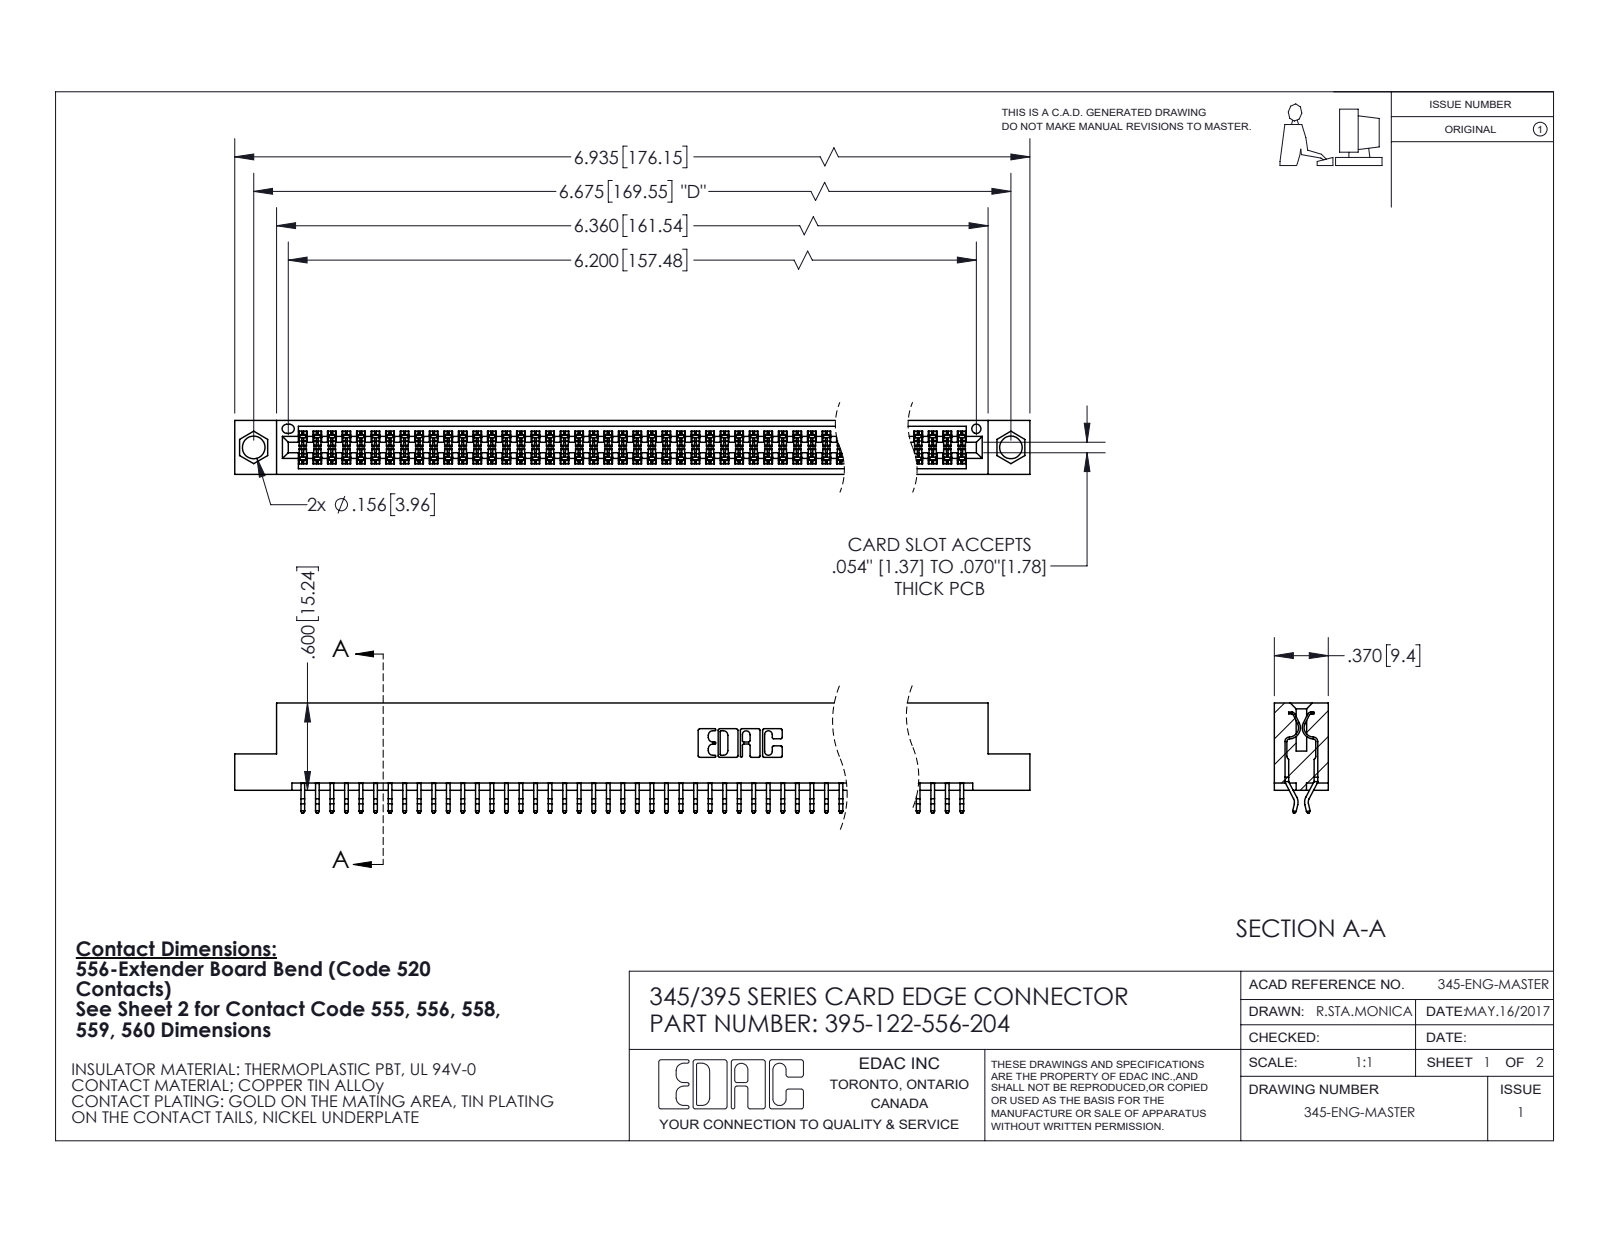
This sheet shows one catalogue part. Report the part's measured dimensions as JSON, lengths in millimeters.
{"part_name": "345-292-001_556 Tail; 395-122-556-204; 345 Part_Flush Mounting Lugs - 0.156 Dia-TI", "step_written_by": "SolidWorks 2020 (CONFIG_CONTROL_DESIGN)", "units": "millimeters", "bodies": {"solids": 123, "faces": 6972, "planar": 4608, "cylindrical": 2364, "other": 0}, "overall_size": [176.1, 19.2, 9.4], "volume_mm3": 17170, "surface_area_mm2": 25500, "round_holes": [[4, 2], [1.6, 1]], "partial_cylinders_radius": [[0.2, 244], [0.3, 22], [0.2, 6], [0.8, 6], [0.7, 3], [0.3, 2], [0.4, 2], [0.5, 2]], "face_to_face_distances": [7.6, 1.8, 9.4, 5.1, 0.6, 2.5, 6.9, 5.7, 4.4, 3.8], "hole_center_spacings": [6.9, 163.6, 169.5]}
